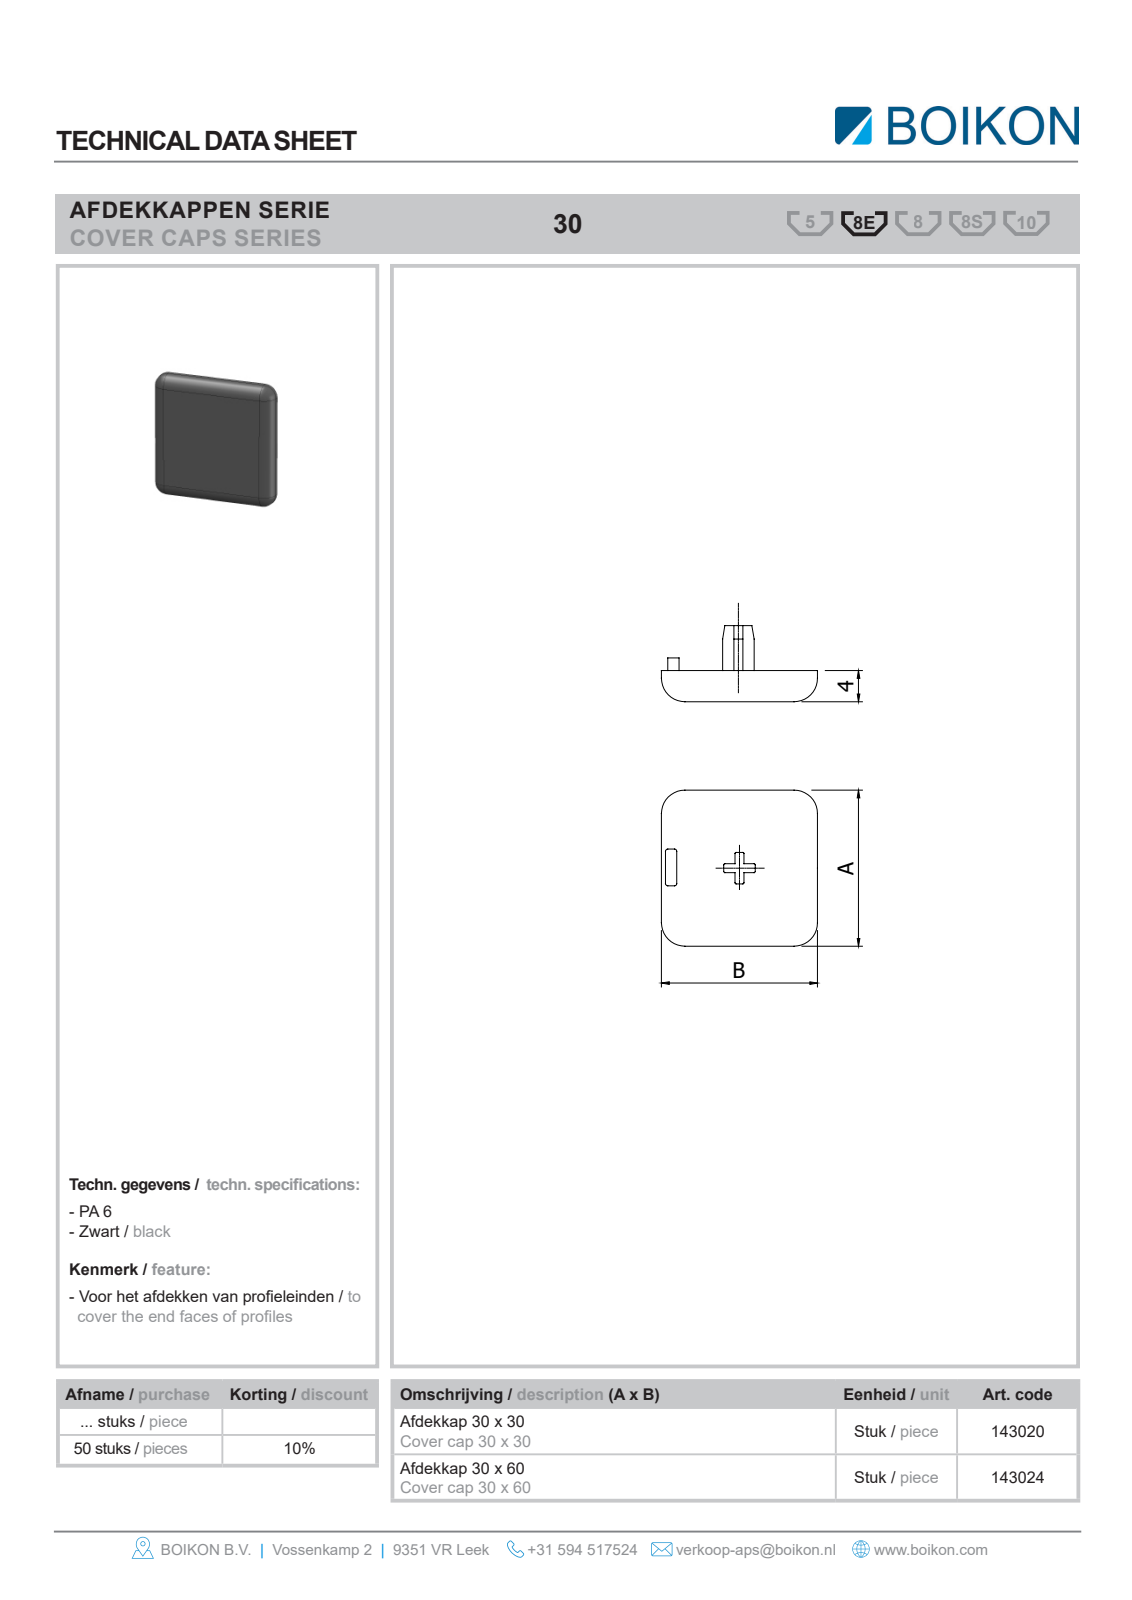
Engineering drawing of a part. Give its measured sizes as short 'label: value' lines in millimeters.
name: Root; 143020 Afdekkap 30 x 30BOIKON
written by: HiCAD 2013 1802.4 Build 509 (AUTOMOTIVE_DESIGN)
unit: mm
bodies: 1 solid, 18 faces (6 planar, 8 cylindrical, 4 other)
size: 30 × 30 × 4
volume: 3 355 mm³; area: 2 092 mm²
rounds: 8× R3
face distances: 4, 30
